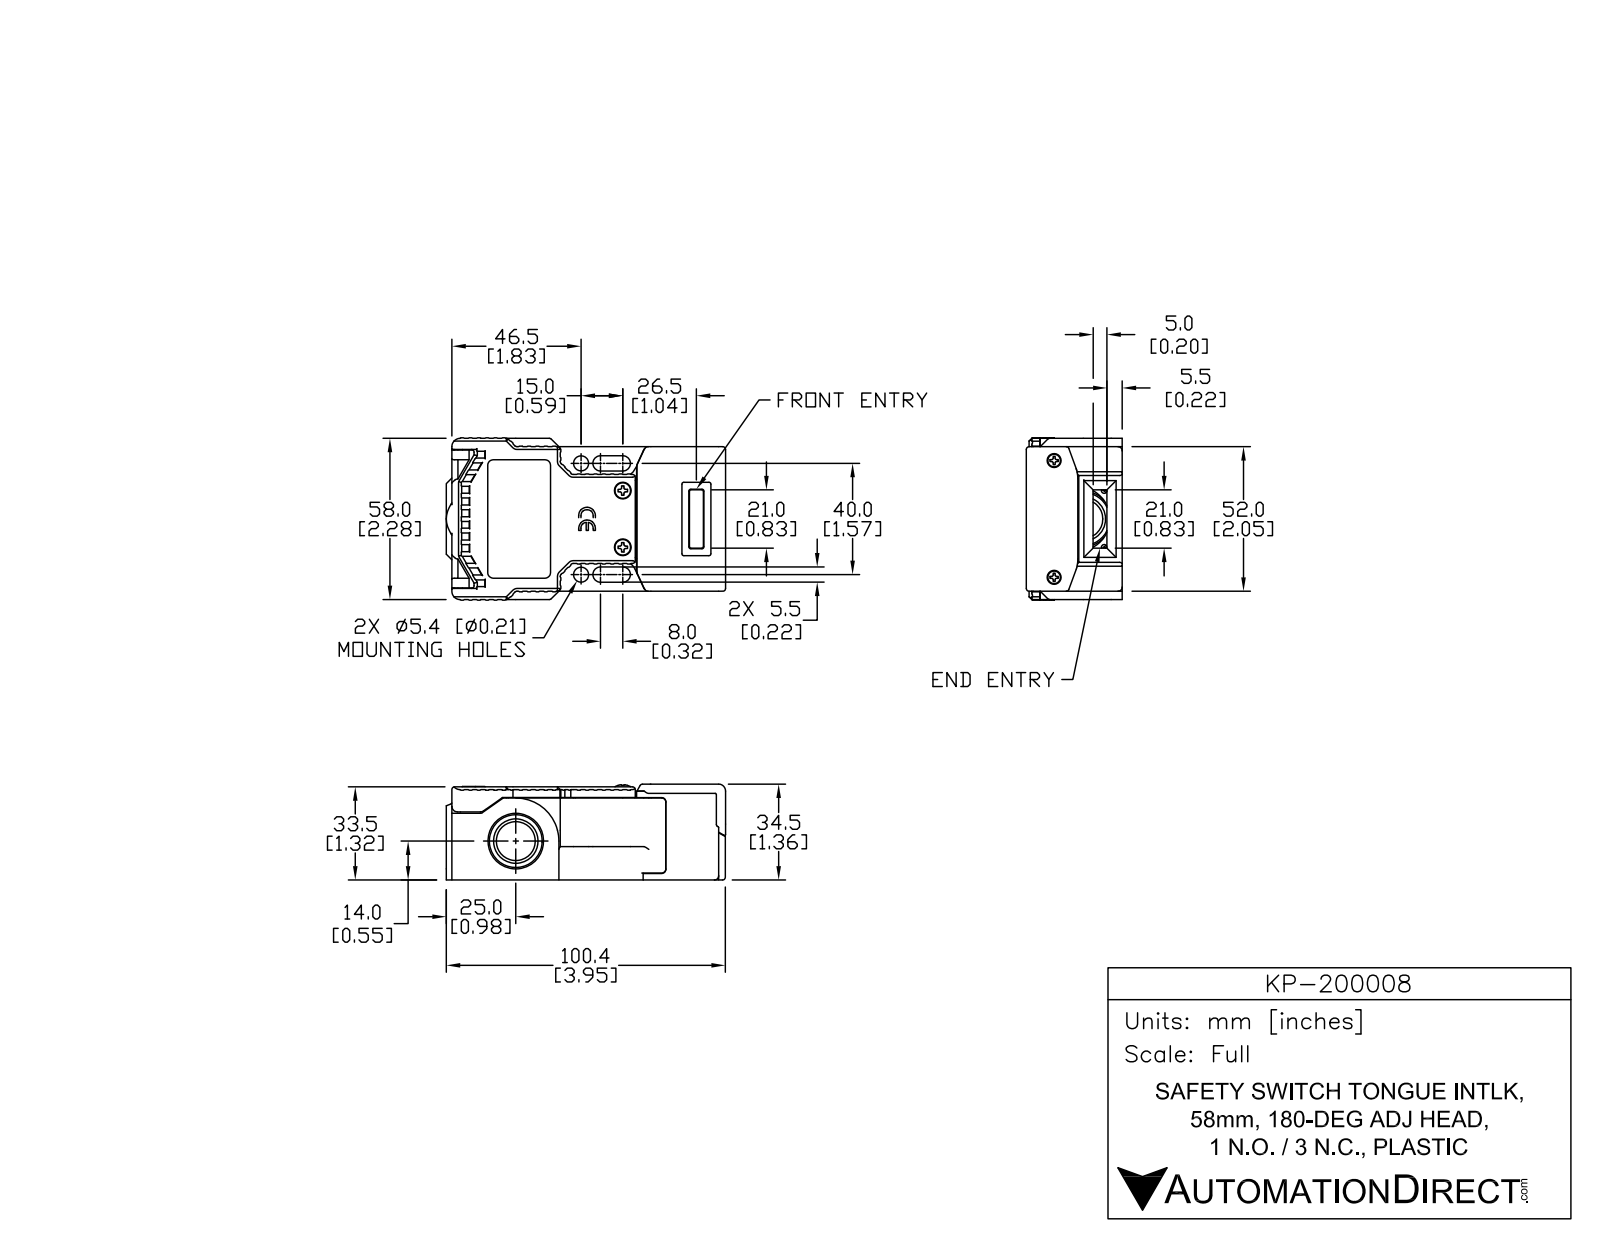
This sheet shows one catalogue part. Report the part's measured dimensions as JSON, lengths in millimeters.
{"part_name": "KP-200008", "step_written_by": "SolidWorks 2013 (AUTOMOTIVE_DESIGN)", "units": "millimeters", "bodies": {"solids": 1, "faces": 206, "planar": 147, "cylindrical": 32, "other": 27}, "overall_size": [101.85, 58, 34.6], "volume_mm3": 158770, "surface_area_mm2": 25501, "round_holes": [[5.4, 2], [19.33, 1], [20, 1]], "round_bosses_or_shafts": [[5.6, 2], [4.5, 2]], "partial_cylinders_radius": [[2, 4], [2.75, 4], [4, 3], [5, 2]], "face_to_face_distances": [33.5, 52, 3, 55, 34.5, 1, 33.45, 1.05, 12.8, 98.5], "hole_center_spacings": [40]}
